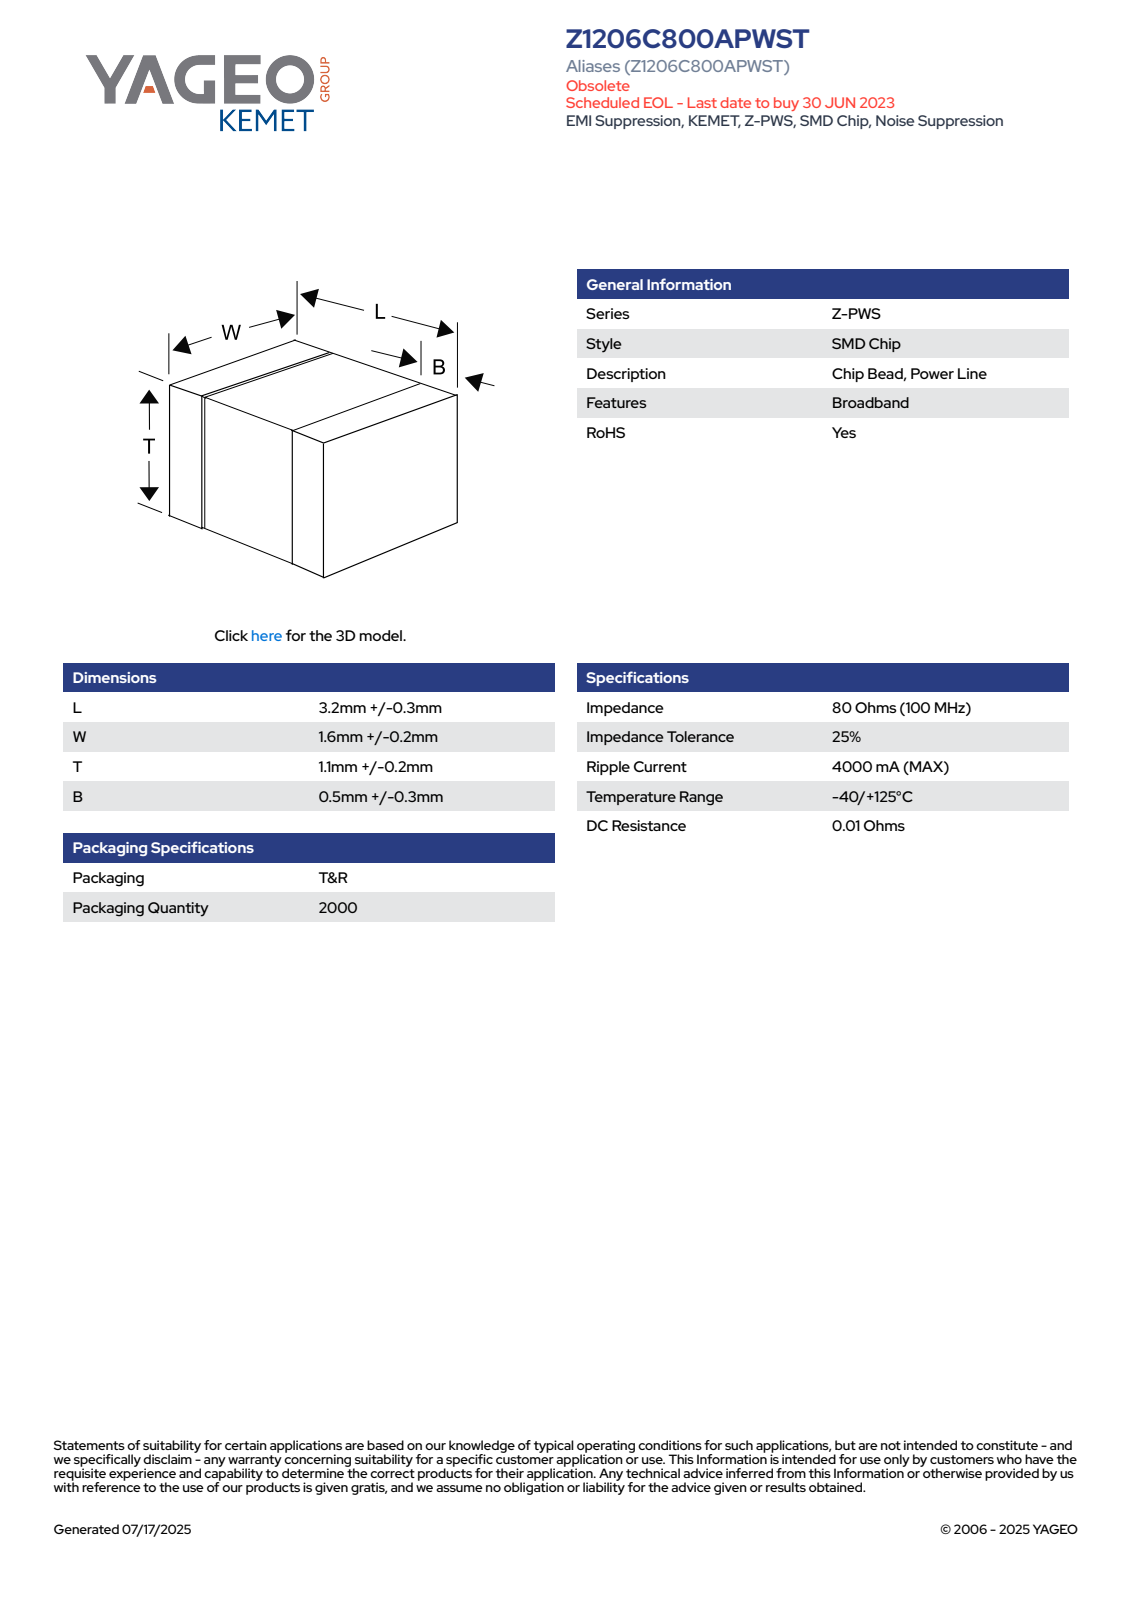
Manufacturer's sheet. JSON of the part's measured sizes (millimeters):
{"part_name": "IS_KCS_1206_L3.5W1.8T1.3B0.8", "step_written_by": "SolidWorks 2014 (AUTOMOTIVE_DESIGN)", "units": "millimeters", "bodies": {"solids": 4, "faces": 73, "planar": 73, "cylindrical": 0, "other": 0}, "overall_size": [3.5, 1.8, 1.3], "volume_mm3": 8, "surface_area_mm2": 27, "face_to_face_distances": [1.28, 1.78, 1.26, 1.3, 1.76, 3.5, 1.8, 0.8, 2.7, 1.9]}
